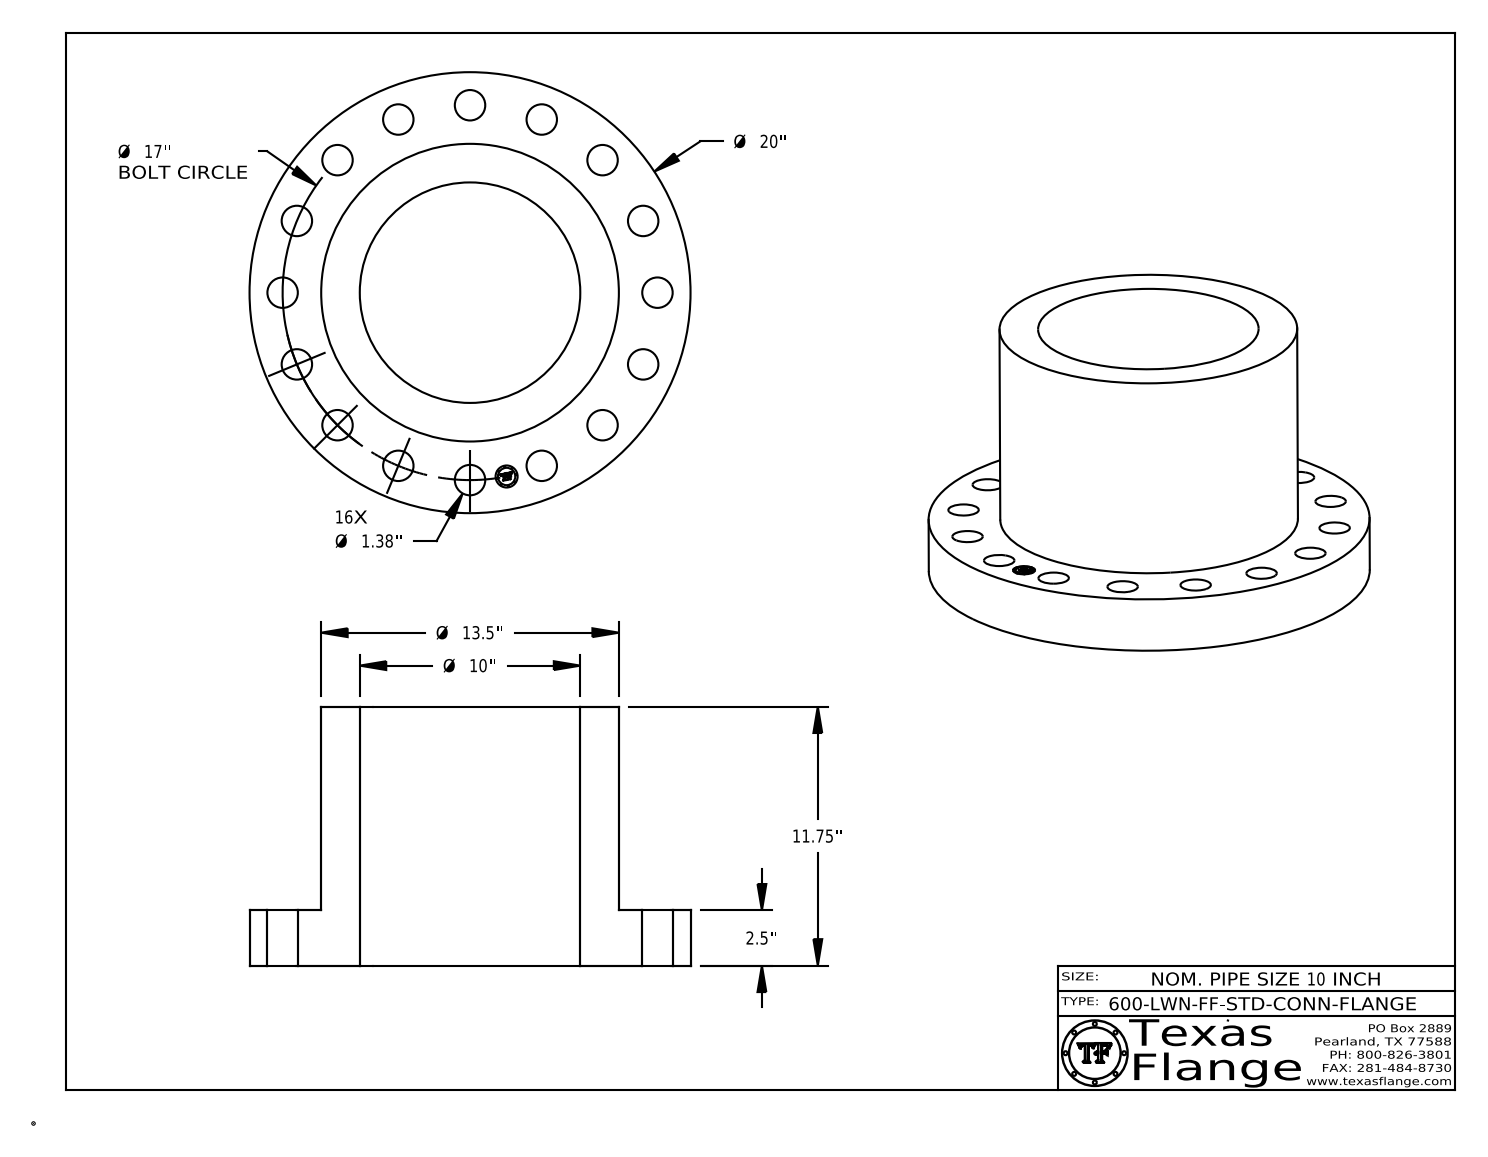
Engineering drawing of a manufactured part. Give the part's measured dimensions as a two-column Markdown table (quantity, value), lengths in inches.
| quantity | value |
| --- | --- |
| part name | 10-600-LWN-FF-STD-CONN-FLANGE |
| STEP written by | CATIA V5 STEP AP214 (AUTOMOTIVE_DESIGN) |
| units | inches |
| bodies | 1 solid, 426 faces (368 planar, 58 cylindrical, 0 other) |
| overall size | 20 × 20 × 11.75 |
| volume | 1 127 in³ |
| surface area | 1 515 in² |
| round holes (diameter × count) | 1.38 × 16, 1 × 1, 10 × 1 |
| round bosses / shafts (diameter × count) | 0.061 × 8, 20 × 1, 13.5 × 1, 0.788 × 1 |
| main face-to-face distances | 2.5, 11.75, 9.25, 2.495, 9.255, 0.298, 0.293, 0.054, 0.193, 0.248 |
| hole center spacings | 3.317, 14.135, 8.5, 6.506, 12.021, 9.444, 9.445, 15.706 |
